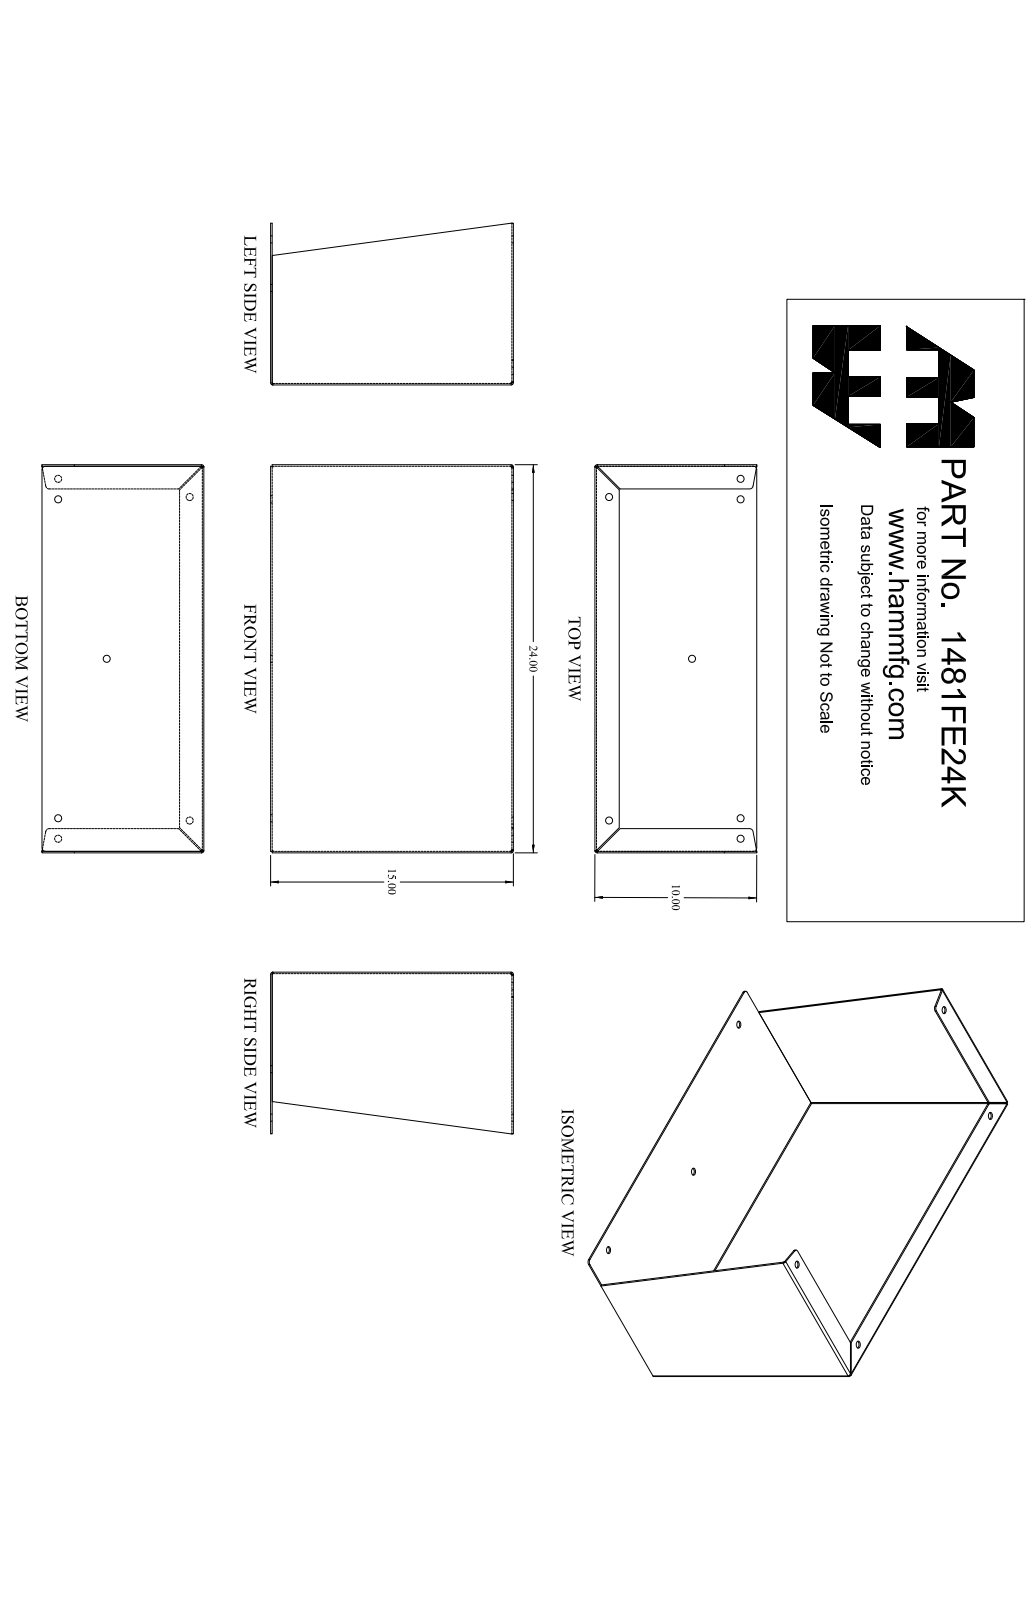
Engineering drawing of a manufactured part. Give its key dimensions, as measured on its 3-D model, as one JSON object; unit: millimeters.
{"part_name": "1481FE24K_Default", "step_written_by": "SolidWorks 2019 (CONFIG_CONTROL_DESIGN)", "units": "millimeters", "bodies": {"solids": 1, "faces": 78, "planar": 42, "cylindrical": 30, "other": 6}, "overall_size": [609.6, 381, 254], "volume_mm3": 1421000, "surface_area_mm2": 1187000, "round_holes": [[11.1, 7]], "partial_cylinders_radius": [[1.2, 6], [3.6, 6], [5.6, 4]], "face_to_face_distances": [2.4, 607.2, 2.4, 604.8, 609.6, 376.2, 378.6, 378.6, 381, 35.7], "hole_center_spacings": [206.4, 208.3, 261.8, 285.4, 545, 32.2, 32.2, 292.7]}
